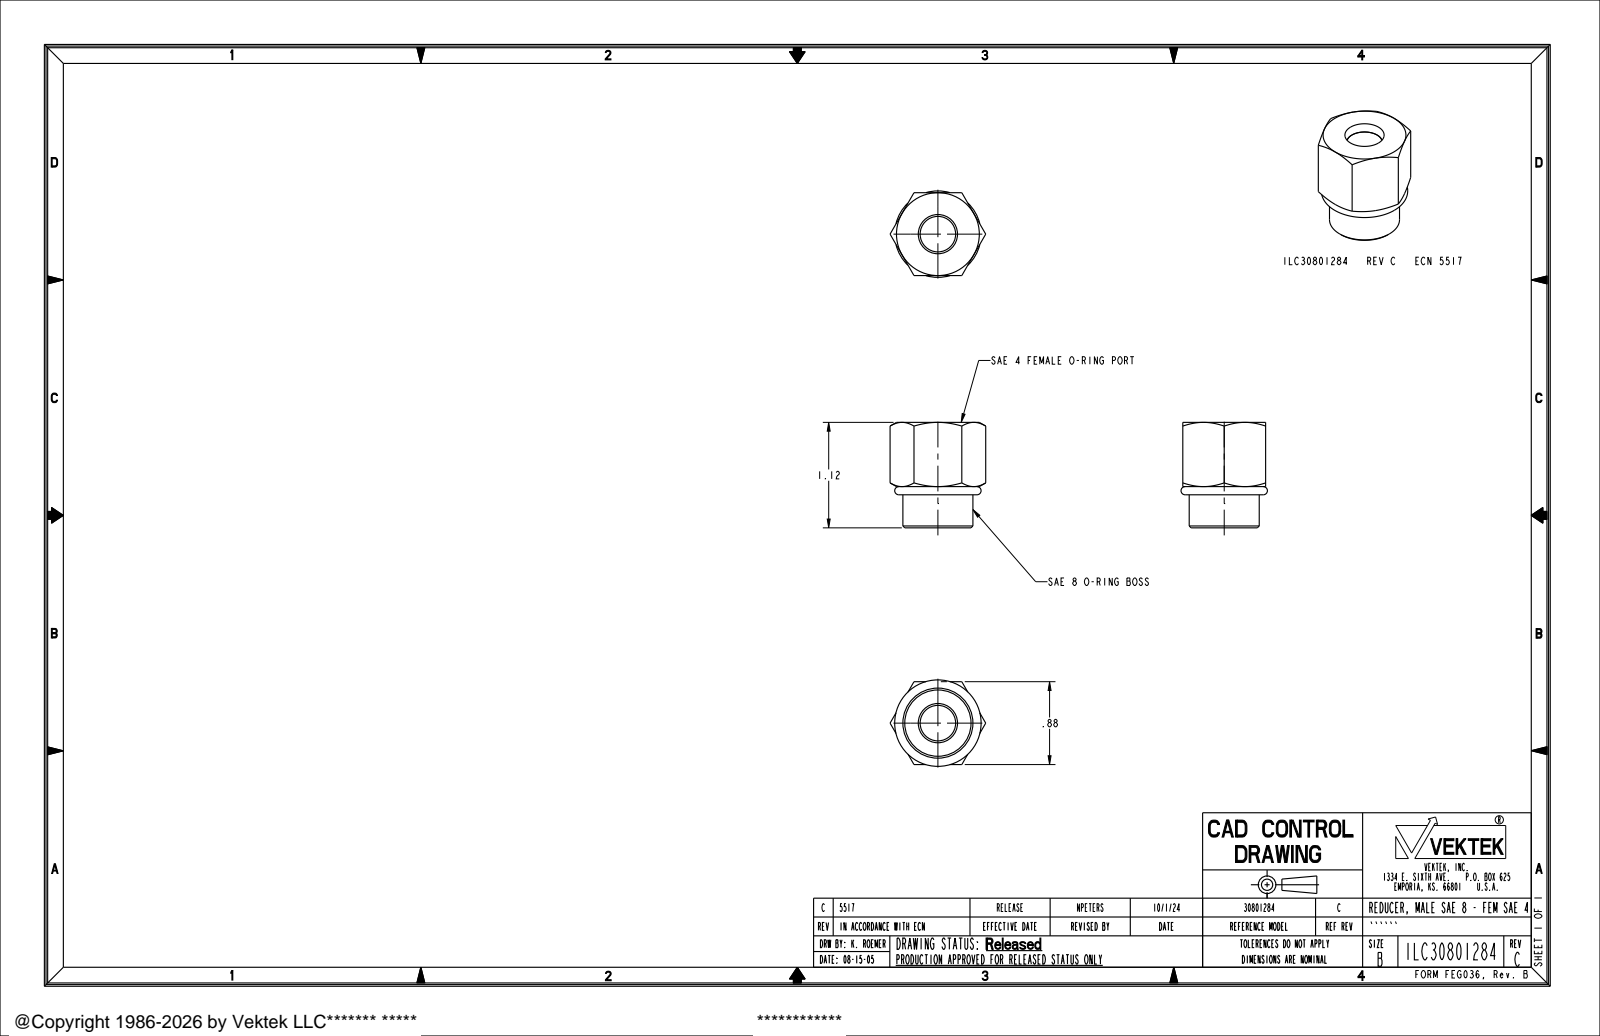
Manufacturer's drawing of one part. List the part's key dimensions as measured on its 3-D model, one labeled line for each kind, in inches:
Part name (STEP PRODUCT): ILC30801284
STEP written by: CREO PARAMETRIC BY PTC INC, 2021164 (AUTOMOTIVE_DESIGN)
Units: inches
Bodies: 1 solid, 40 faces (11 planar, 7 cylindrical, 22 other)
Overall size (bounding box): 1.12 × 1.016 × 0.918
Volume: 0.535 in³ · Surface area: 6.825 in²
Round holes (diameter × count): ⌀0.377 ×1
Round bosses / shafts (diameter × count): ⌀0.744 ×1, ⌀0.41 ×1
Main face-to-face distances: 0.88, 1.12, 0.438, 0.682, 0.527, 0.089, 0.593, 1.027, 0.589, 0.5
